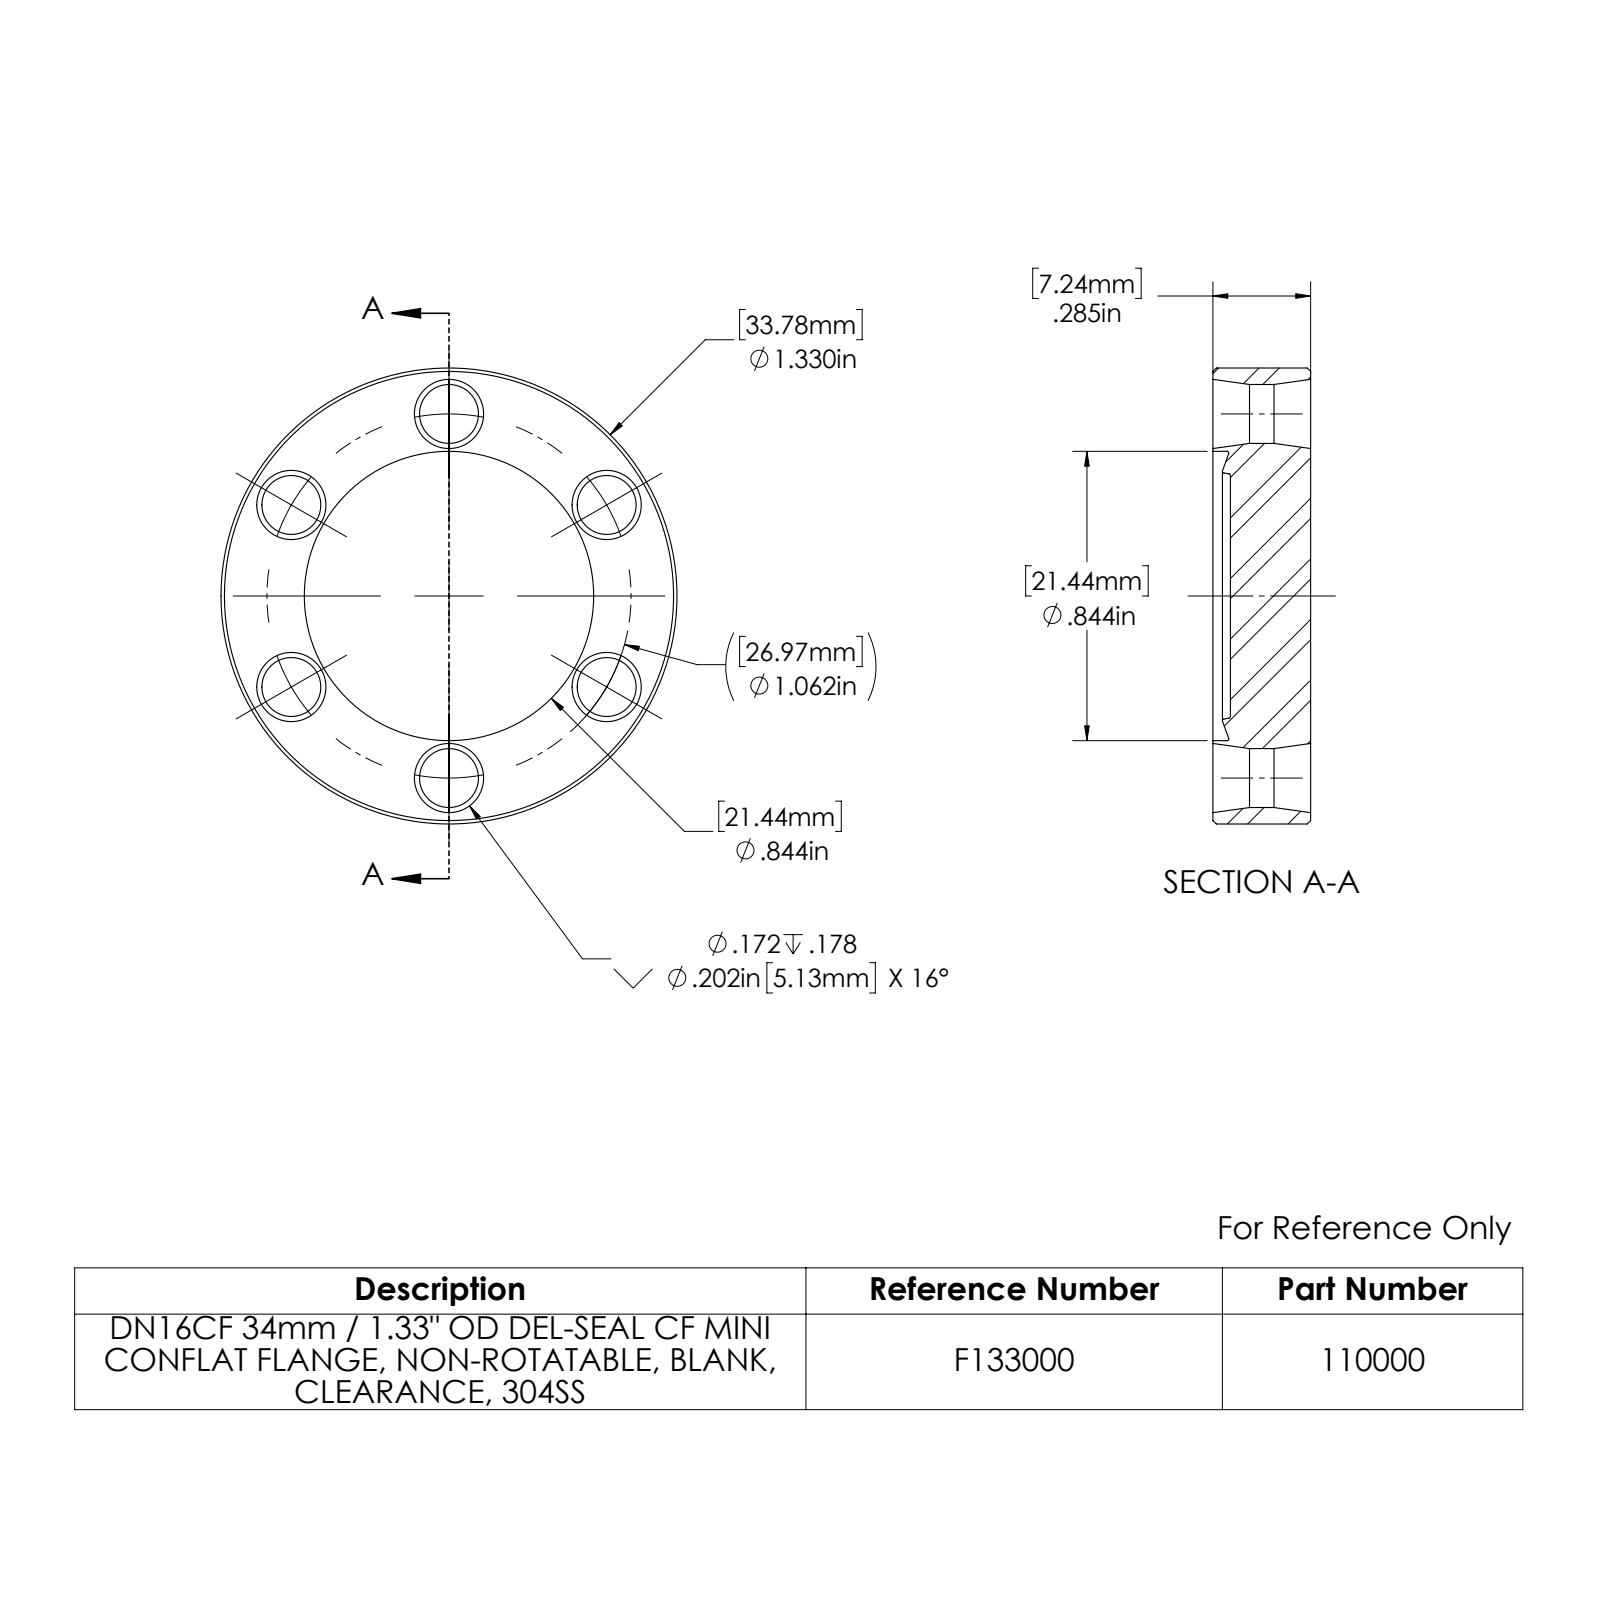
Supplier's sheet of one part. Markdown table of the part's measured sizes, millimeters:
| quantity | value |
| --- | --- |
| part name | 110000 |
| STEP written by | SolidWorks 2022 (AUTOMOTIVE_DESIGN) |
| units | millimeters |
| bodies | 1 solid, 57 faces (3 planar, 16 cylindrical, 38 other) |
| overall size | 33.8 × 33.8 × 7.2 |
| volume | 5 310 mm³ |
| surface area | 3 026 mm² |
| round holes (diameter × count) | 4.4 × 6, 21.4 × 1 |
| round bosses / shafts (diameter × count) | 33.8 × 1 |
| main face-to-face distances | 7.2, 1.3, 5.9 |
| hole center spacings | 13.5, 23.4, 13.5, 27, 27 |
